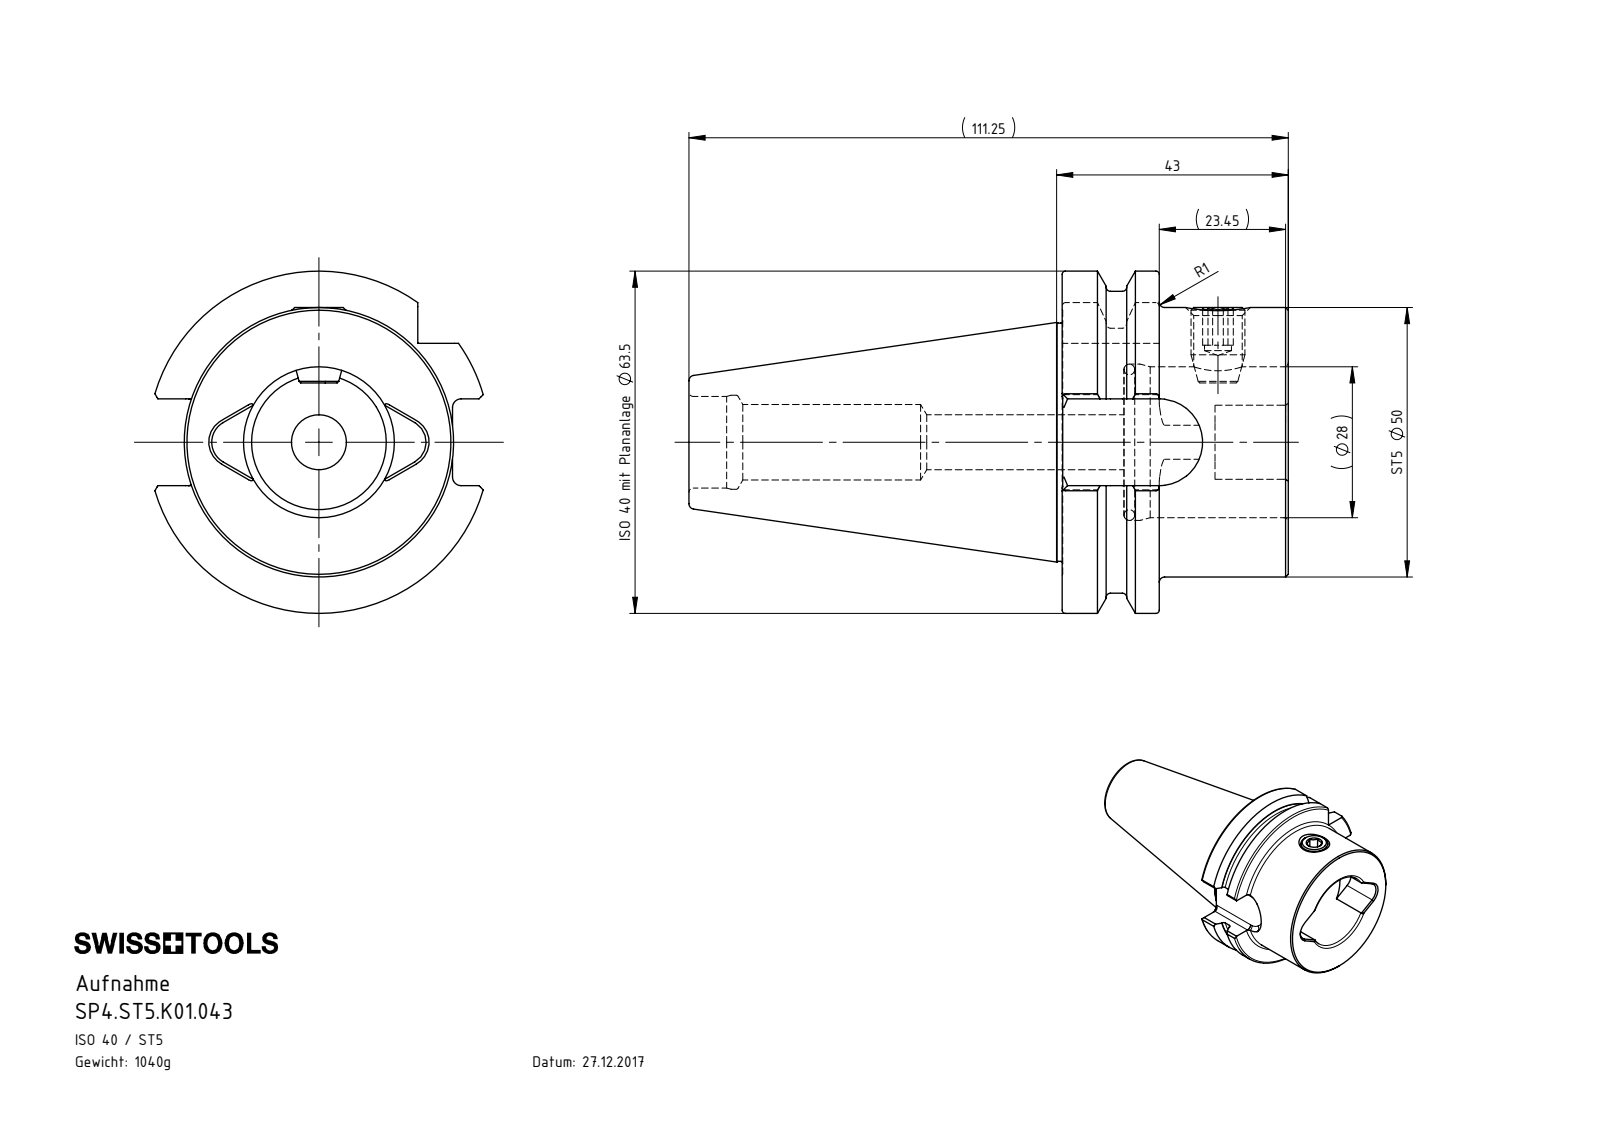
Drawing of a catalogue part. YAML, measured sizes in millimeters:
part_name: "SP4-ST5.K01.043_A_Fertigbearbeitung; SP4.ST5.K01.043; DIN 3771 - 25x2; ST5-ER1.001.012_A"
step_written_by: "SolidWorks 2017 (AUTOMOTIVE_DESIGN)"
units: millimeters
bodies: {solids: 3, faces: 147, planar: 56, cylindrical: 36, other: 55}
overall_size: [111.25, 63.5, 60.94]
volume: 132672
surface_area: 27666
round_holes:
  - {diameter: 5, count: 1}
  - {diameter: 9, count: 1}
  - {diameter: 10.2, count: 1}
  - {diameter: 14, count: 1}
  - {diameter: 17, count: 1}
  - {diameter: 17.45, count: 1}
  - {diameter: 28, count: 1}
  - {diameter: 29, count: 1}
round_bosses_or_shafts:
  - {diameter: 50, count: 1}
  - {diameter: 44.45, count: 1}
  - {diameter: 44.2, count: 1}
  - {diameter: 10, count: 1}
partial_cylinders:
  - {radius: 1.6, count: 8}
  - {radius: 4.2, count: 2}
  - {radius: 8, count: 1}
  - {radius: 8.05, count: 1}
  - {radius: 28, count: 1}
  - {radius: 31.75, count: 1}
face_to_face_distances: [41.97, 18.02, 23.95, 11.47, 6.55, 30.5, 47.4, 11.37, 17.92, 41.87]
